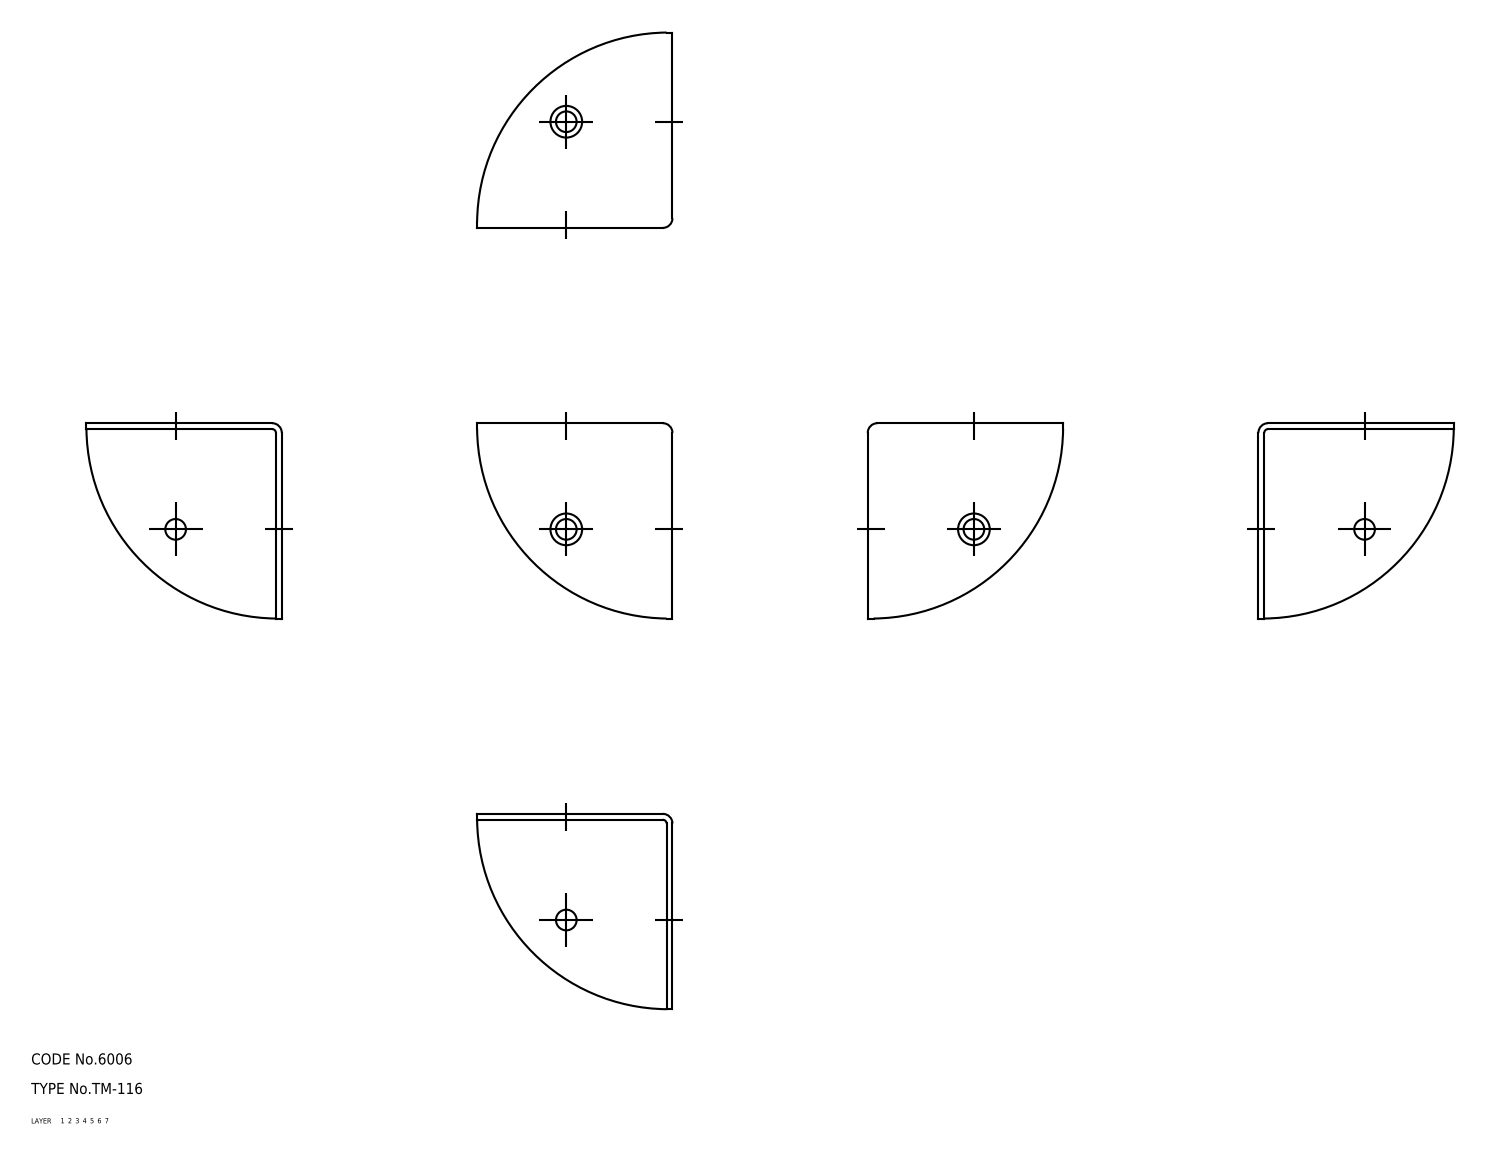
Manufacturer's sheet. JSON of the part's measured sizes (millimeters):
{"part_name": "angle", "step_written_by": "CADfix (AUTOMOTIVE_DESIGN)", "units": "millimeters", "bodies": {"solids": 1, "faces": 32, "planar": 0, "cylindrical": 0, "other": 32}, "overall_size": [53, 53, 53], "volume_mm3": 9913, "surface_area_mm2": 12918}
